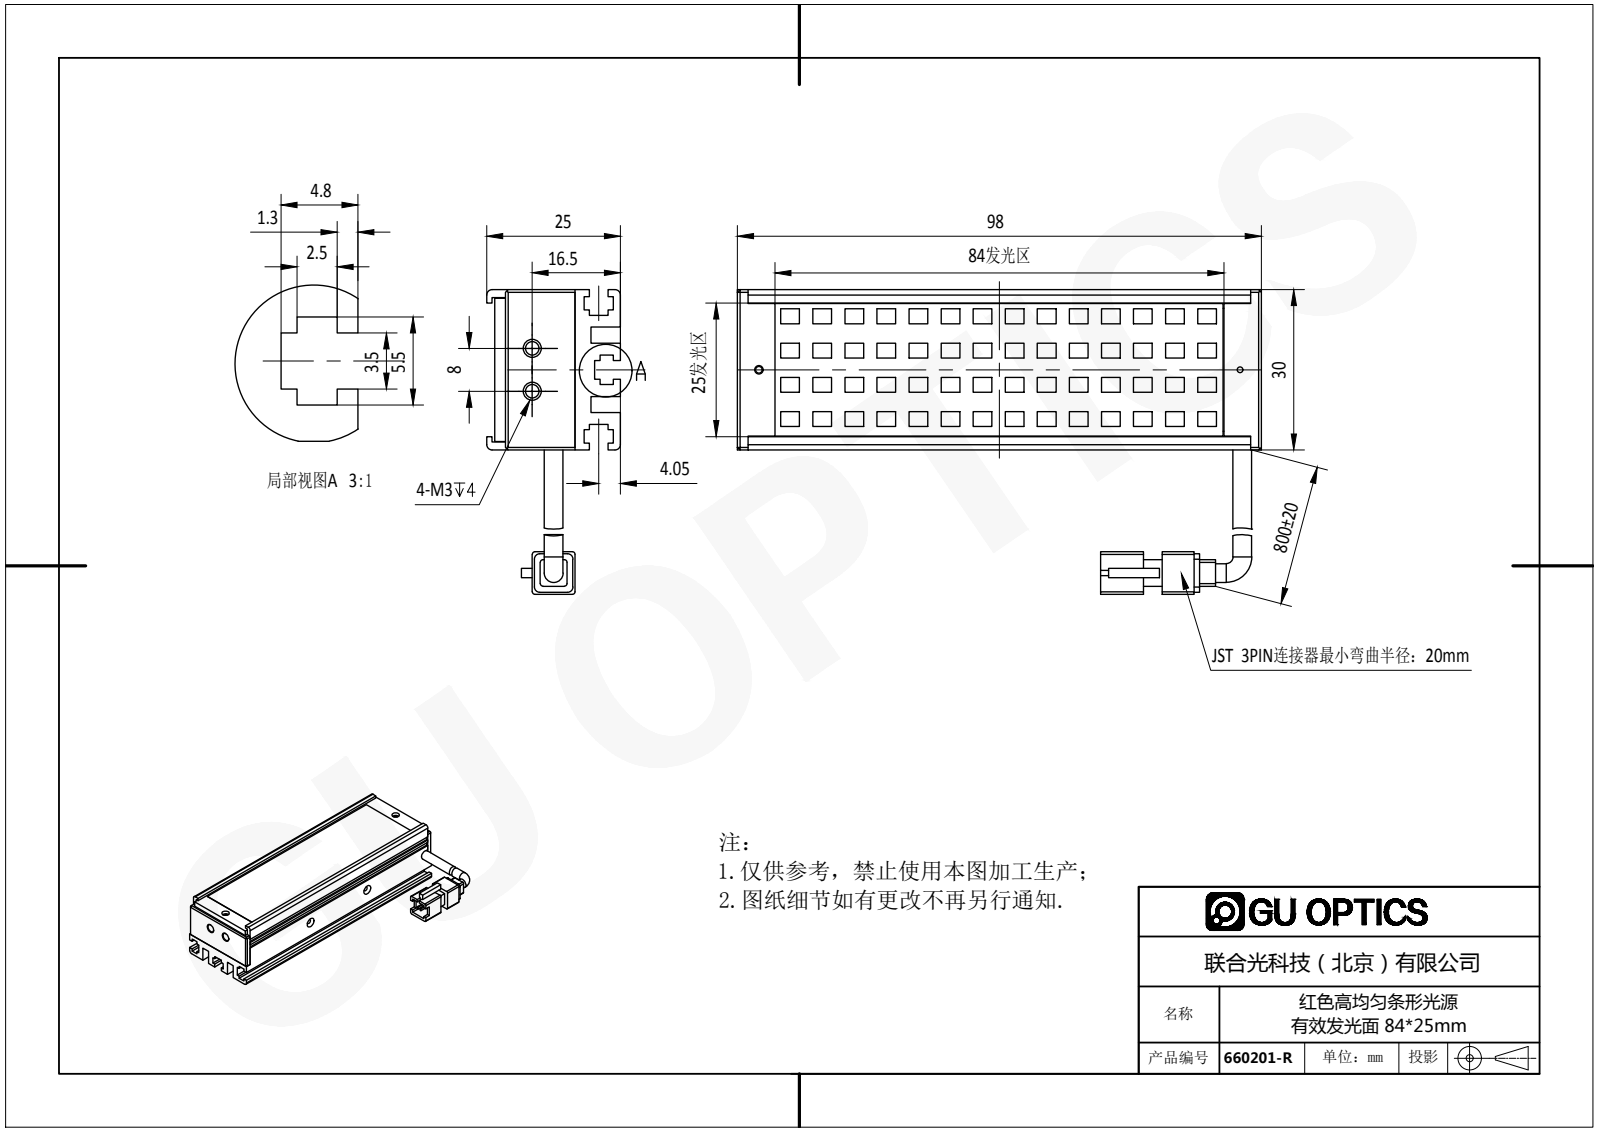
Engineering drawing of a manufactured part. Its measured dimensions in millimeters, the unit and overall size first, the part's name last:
Units: millimetres
Overall size (bounding box): 98 × 57 × 25
Round holes (diameter × count): ⌀1.6 ×5, ⌀1.5 ×2, ⌀1.7 ×2, ⌀2.5 ×2, ⌀2.8 ×2, ⌀3 ×2, ⌀1.1 ×1, ⌀1.25 ×1, ⌀2 ×1
Round bosses / shafts (diameter × count): ⌀3.5 ×2
Partial cylindrical surfaces — rounded edges, fillets, slot ends (radius × count): R1 ×12, R0.5 ×8, R1.65 ×1
Main face-to-face distances: 1, 13, 2, 2.5, 3, 9.5, 2.1, 4.5, 27.5, 8.5
Hole centre spacings: 30, 90, 7, 30.72, 60, 60.36, 90.27, 8
Volume: 36 231 mm³ · Surface area: 36 407 mm²
Bodies: 6 solids, 724 faces (538 planar, 83 cylindrical, 103 other)
Part name (STEP PRODUCT): 660201-R
STEP written by: SolidWorks 2016 (AUTOMOTIVE_DESIGN)
